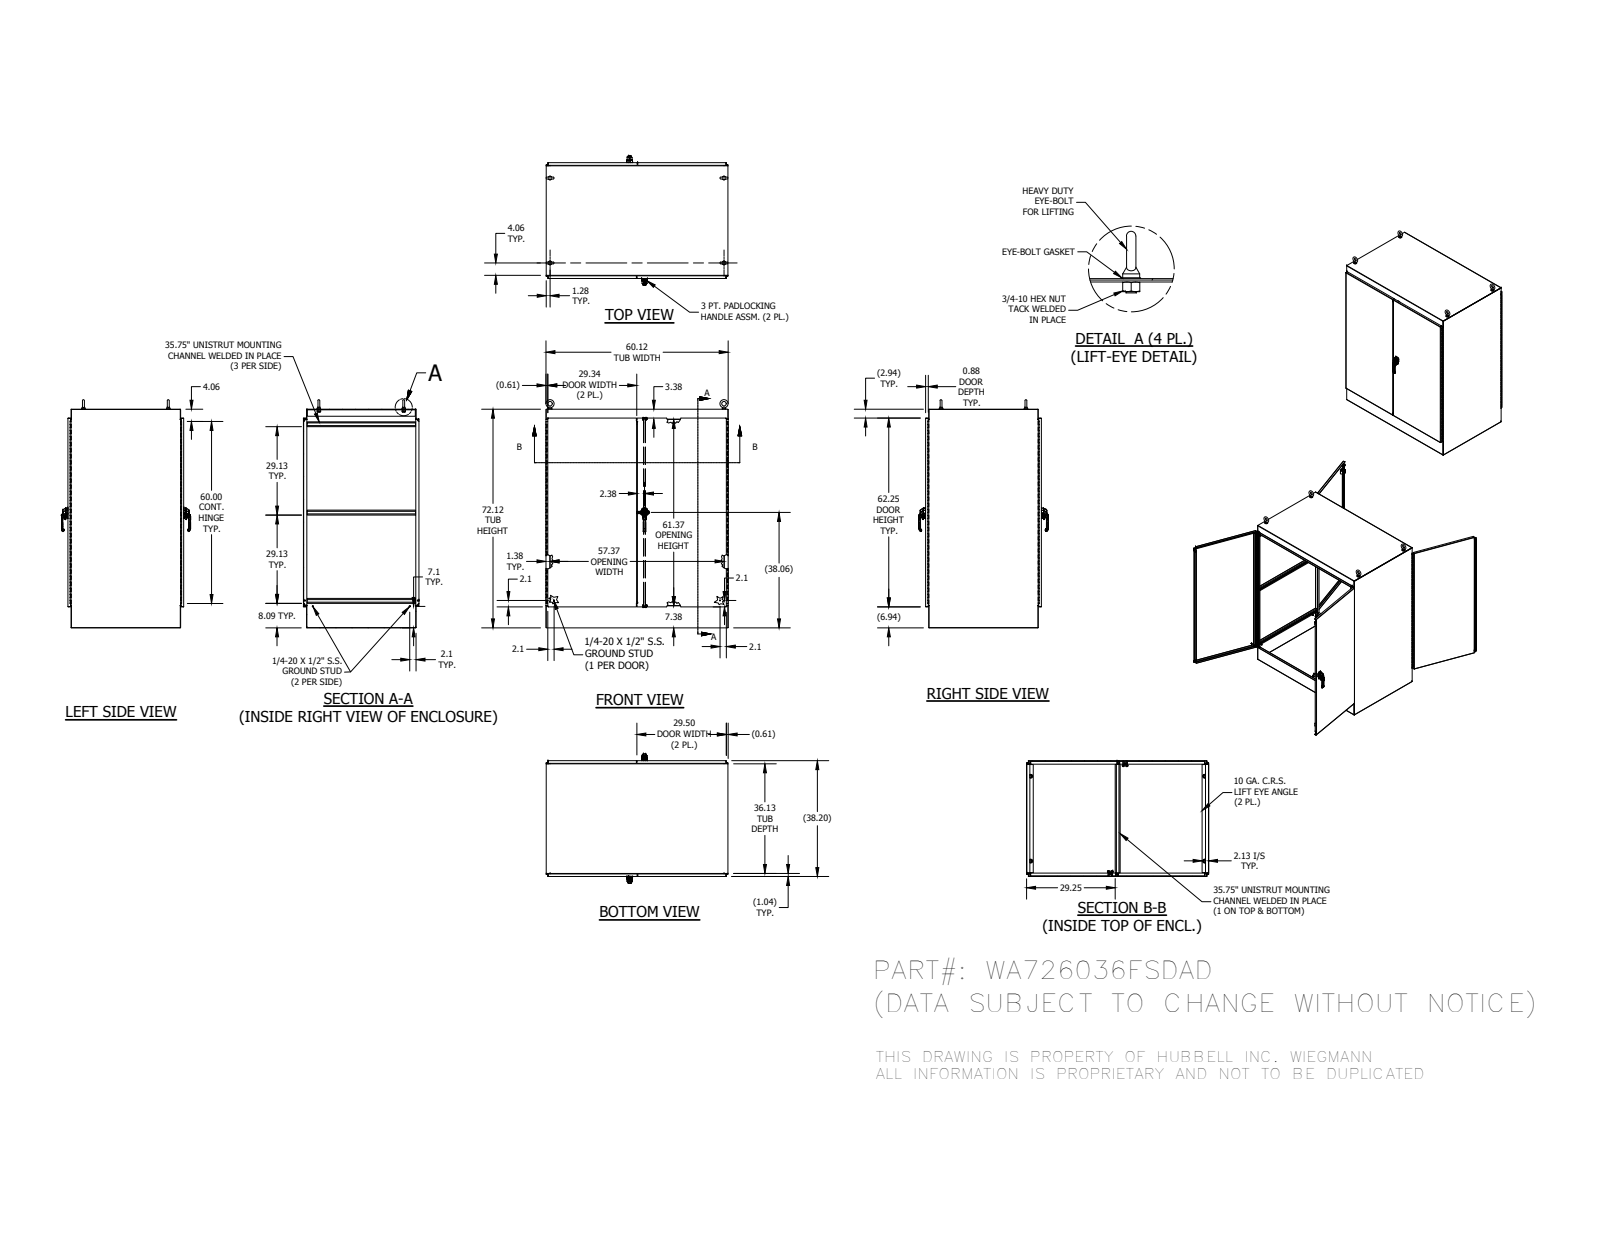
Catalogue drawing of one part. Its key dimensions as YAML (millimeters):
part_name: "FUN00105; HFW3025; 316298; 349132 (+8 more)"
step_written_by: "Autodesk Inventor 2014 (AUTOMOTIVE_DESIGN)"
units: millimeters
bodies: {solids: 116, faces: 7392, planar: 3430, cylindrical: 2482, other: 1480}
overall_size: [1911.29, 1527.17, 1085.41]
volume: 35970000
surface_area: 29390000
round_holes:
  - {diameter: 7.02, count: 16}
  - {diameter: 5.08, count: 8}
  - {diameter: 20.64, count: 8}
  - {diameter: 5.4, count: 6}
  - {diameter: 6, count: 6}
  - {diameter: 7.11, count: 6}
  - {diameter: 3.17, count: 4}
  - {diameter: 6.13, count: 4}
  - {diameter: 6.35, count: 4}
  - {diameter: 6.41, count: 4}
  - {diameter: 10.16, count: 4}
  - {diameter: 10.33, count: 4}
round_bosses_or_shafts:
  - {diameter: 6.35, count: 8}
  - {diameter: 31.75, count: 4}
  - {diameter: 28.45, count: 4}
  - {diameter: 25.4, count: 4}
  - {diameter: 19.05, count: 4}
  - {diameter: 14.29, count: 4}
  - {diameter: 13.37, count: 4}
  - {diameter: 12.7, count: 4}
partial_cylinders:
  - {radius: 0.5, count: 345}
  - {radius: 0.3, count: 170}
  - {radius: 0.79, count: 46}
  - {radius: 0.47, count: 38}
  - {radius: 0.25, count: 32}
  - {radius: 2, count: 30}
  - {radius: 3.17, count: 30}
  - {radius: 3, count: 29}
face_to_face_distances: [2.38, 967.79, 1524.8, 1829.6, 965.41, 970.17, 26.3, 941.49, 1522.42, 1527.18]
hole_center_spacings: [711.2, 6.5, 12.5, 22.5, 51.5, 124.7, 126.71, 0.8]
